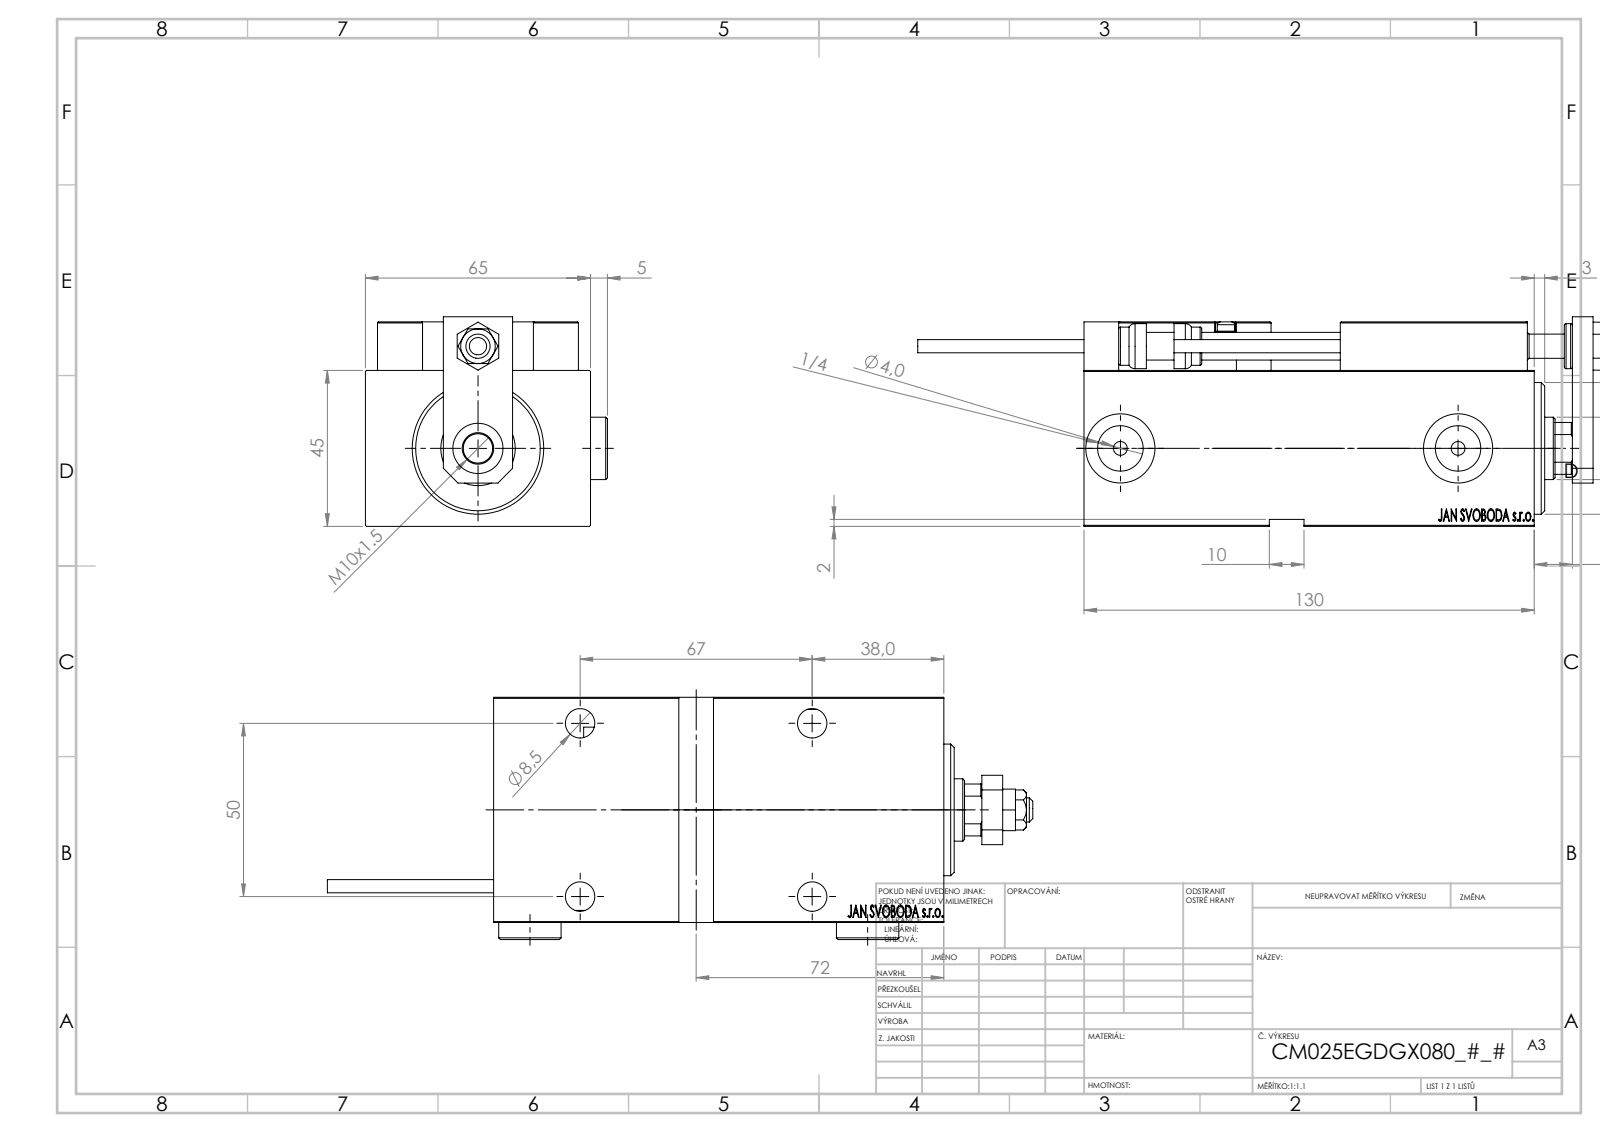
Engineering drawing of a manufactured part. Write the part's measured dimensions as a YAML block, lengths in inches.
part_name: "NUT_D10; ALLEN BOLT D8; ALLEN BOLT D5; SWITCH_X_FRONT_BACK (+7 more)"
step_written_by: "SolidWorks 2019 (CONFIG_CONTROL_DESIGN)"
units: inches
bodies: {solids: 26, faces: 1347, planar: 604, cylindrical: 198, other: 545}
overall_size: [8.02, 2.752, 2.382]
volume: 24.1
surface_area: 144.1
round_holes:
  - {diameter: 0.157, count: 6}
  - {diameter: 0.315, count: 5}
  - {diameter: 0.335, count: 5}
  - {diameter: 0.126, count: 4}
  - {diameter: 0.531, count: 4}
  - {diameter: 0.197, count: 2}
  - {diameter: 0.518, count: 2}
  - {diameter: 0.787, count: 2}
  - {diameter: 0.276, count: 1}
  - {diameter: 0.571, count: 1}
  - {diameter: 0.709, count: 1}
  - {diameter: 0.846, count: 1}
round_bosses_or_shafts:
  - {diameter: 0.709, count: 2}
  - {diameter: 0.197, count: 2}
  - {diameter: 0.15, count: 2}
  - {diameter: 1.496, count: 1}
  - {diameter: 1.063, count: 1}
  - {diameter: 0.512, count: 1}
  - {diameter: 0.433, count: 1}
partial_cylinders:
  - {radius: 0.012, count: 30}
  - {radius: 0.118, count: 2}
  - {radius: 0.335, count: 1}
face_to_face_distances: [1.772, 2.559, 0.551, 0.236, 2.323, 0.512, 5.118, 0.138, 0.197, 5.551]
hole_center_spacings: [1.587, 0.448, 0.787, 0.984, 1.165, 1.169, 1.356, 1.42]
